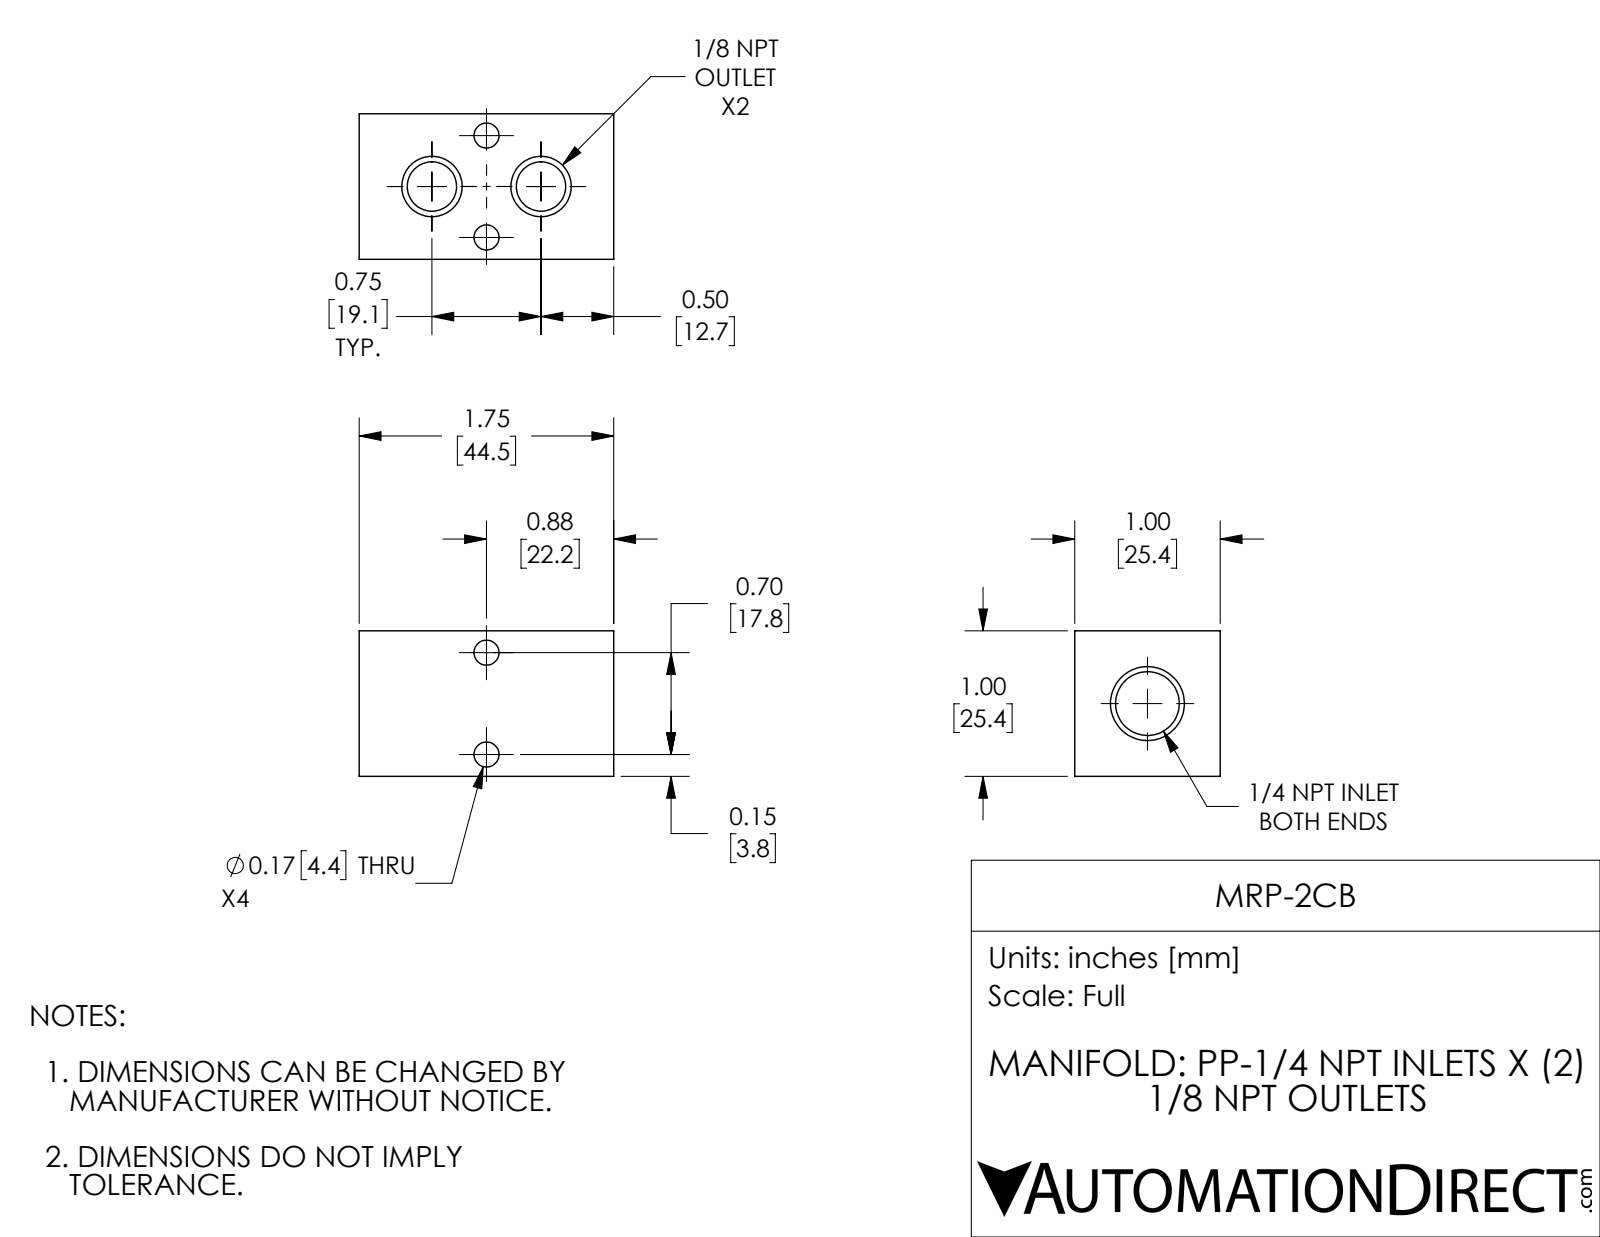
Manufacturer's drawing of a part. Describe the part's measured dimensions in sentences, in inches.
The part is named "MRP-2CB". Its 3-D file was written by "SolidWorks 2018 (AUTOMOTIVE_DESIGN)". It is 1 solid with 44 faces: 6 planar, 30 cylindrical and 8 other. Overall it measures 1.75 by 1 by 1 inches. Its volume is 1.35 cubic inches and its surface area 12.81 square inches. Round holes: 4 of diameter 0.172, 2 of diameter 0.339, 1 of diameter 0.438. The main face-to-face distances are 1, 1.75. The hole center spacings are 0.513, 0.7, 0.75.
